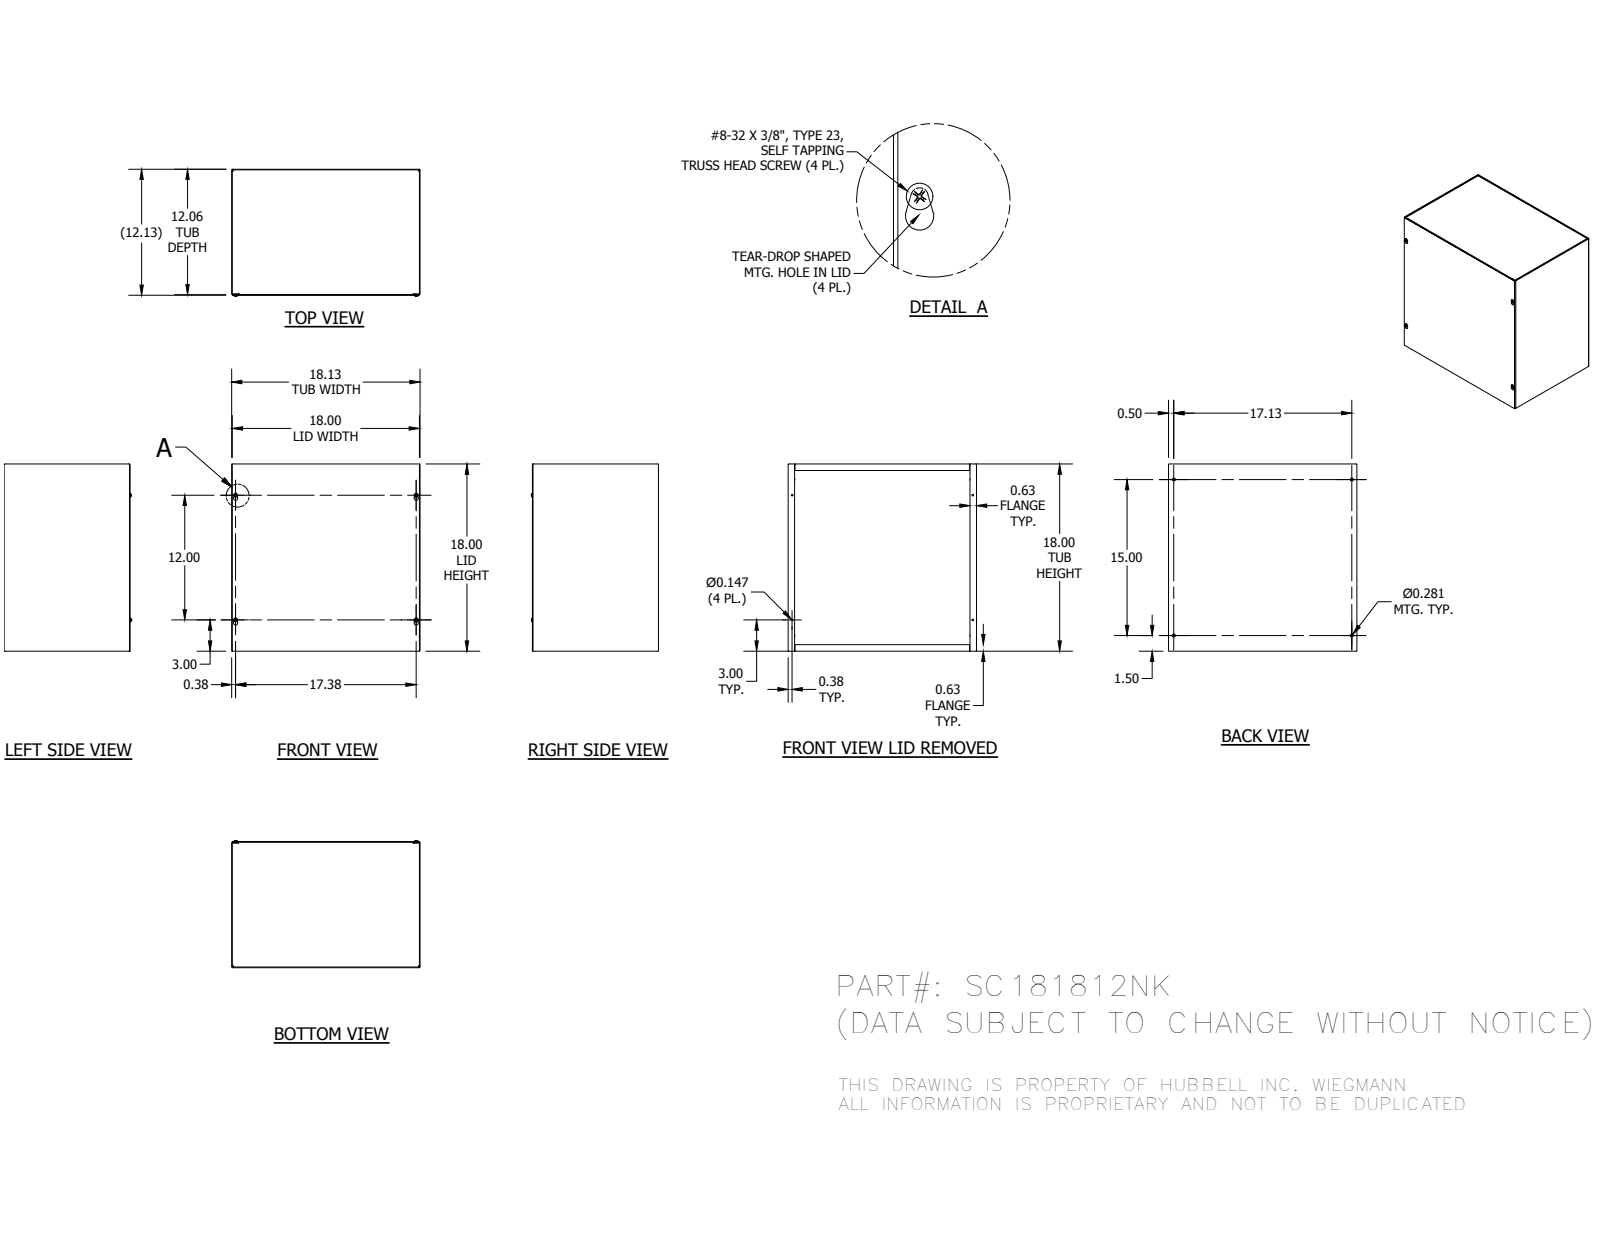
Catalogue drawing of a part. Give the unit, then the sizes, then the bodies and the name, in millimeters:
Units: millimetres
Overall size (bounding box): 460.38 × 457.2 × 310.52
Round holes (diameter × count): ⌀3.73 ×4, ⌀7.14 ×4
Round bosses / shafts (diameter × count): ⌀9.75 ×4, ⌀4.17 ×4
Partial cylindrical surfaces — rounded edges, fillets, slot ends (radius × count): R0.79 ×12, R2.38 ×12, R3.17 ×4, R5.16 ×4
Main face-to-face distances: 1.59, 306.39, 457.2, 455.61, 458.79, 304.8, 307.98, 454.02, 460.38, 3.18
Hole centre spacings: 38.23, 342.91, 439.8, 556.38, 304.8, 381, 434.98, 441.32
Volume: 1 633 000 mm³ · Surface area: 2 071 000 mm²
Bodies: 8 solids, 268 faces (152 planar, 48 cylindrical, 68 other)
Part name (STEP PRODUCT): SC181812NKBLR; SC1812NKTB; SC1818LPA; 34056 (+1 more)
STEP written by: Autodesk Inventor 2014 (AUTOMOTIVE_DESIGN)
